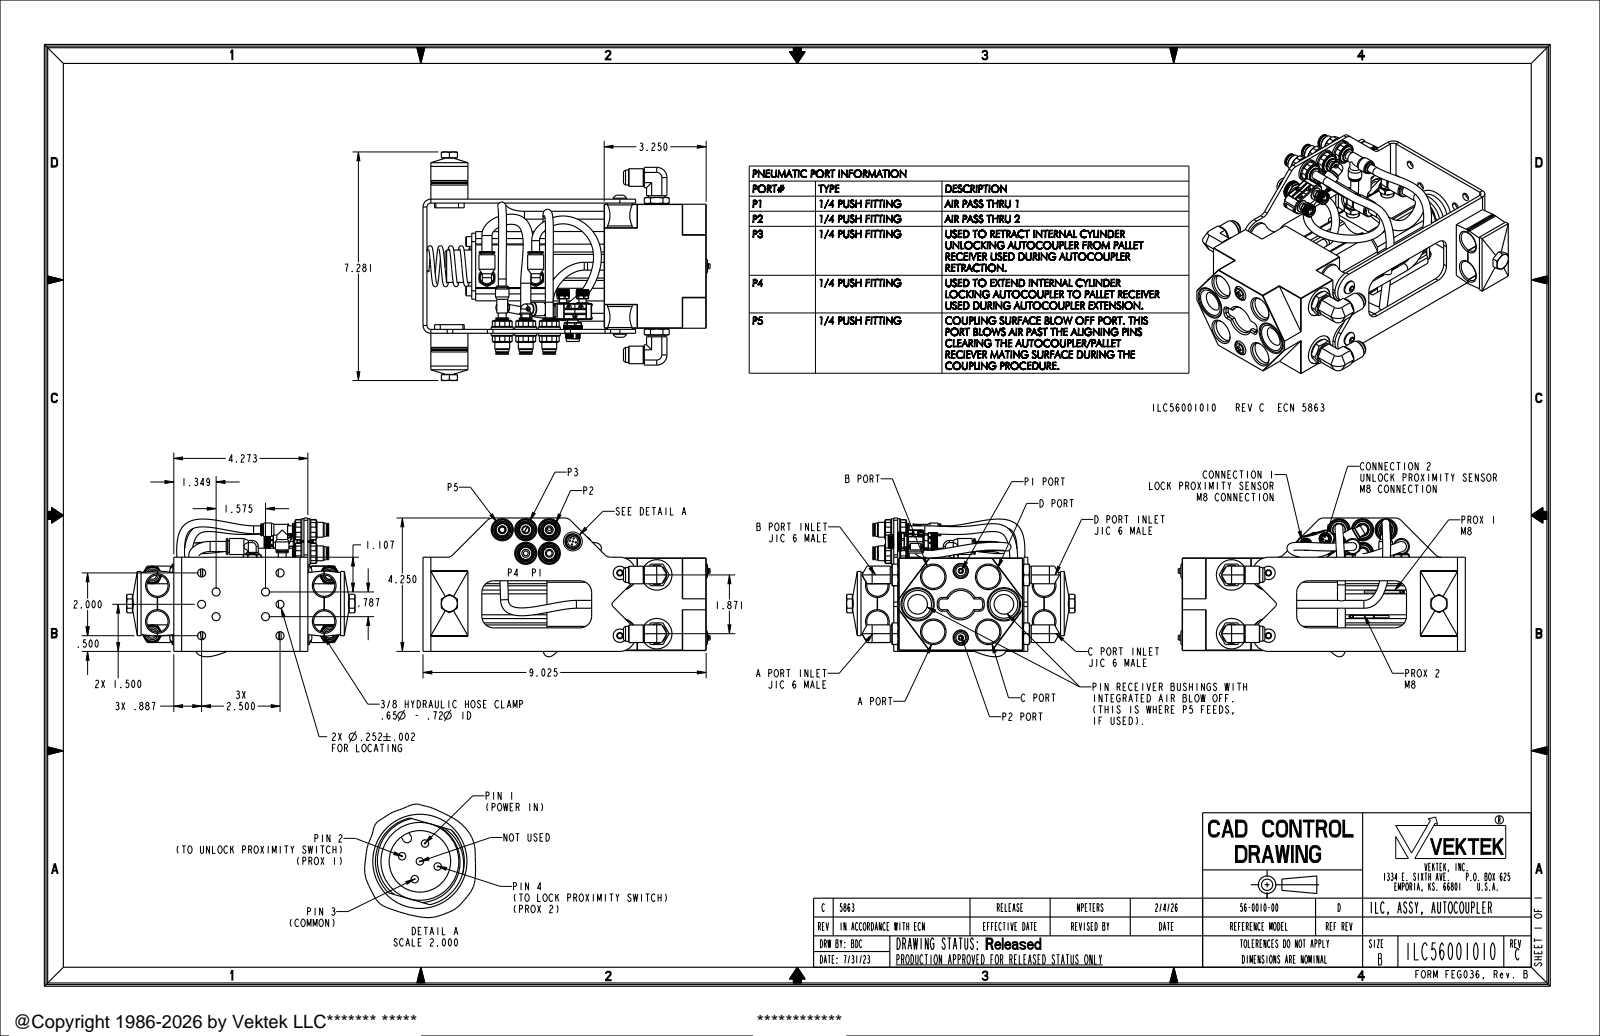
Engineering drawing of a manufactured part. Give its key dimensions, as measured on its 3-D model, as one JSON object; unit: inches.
{"part_name": "ILC56001010", "step_written_by": "CREO PARAMETRIC BY PTC INC, 2021164 (AUTOMOTIVE_DESIGN)", "units": "inches", "bodies": {"solids": 9, "faces": 3105, "planar": 1493, "cylindrical": 844, "other": 768}, "overall_size": [9.15, 7.281, 4.421], "volume_in3": 66.93, "surface_area_in2": 386.1, "round_holes": [[0.25, 10], [0.257, 8], [0.047, 6], [0.282, 6], [0.31, 4], [0.38, 4], [0.505, 4], [0.677, 4], [0.735, 4], [0.03, 2], [0.098, 2], [0.098, 2]], "round_bosses_or_shafts": [[0.56, 6], [0.411, 6], [0.297, 6], [0.705, 5], [0.551, 5], [0.472, 5], [0.421, 5], [0.039, 5]], "partial_cylinders_radius": [[0.1, 9], [0.021, 6], [0.084, 6], [0.25, 6], [0.008, 5], [0.326, 5], [0.375, 5], [0.01, 4]], "face_to_face_distances": [0.125, 0.125, 4.273, 4.148, 4.148, 4.023, 2.95, 0.037, 3.986, 1.428], "hole_center_spacings": [0.069, 0.75, 0.097, 0.396, 0.489, 0.895, 0.915, 1.068]}
